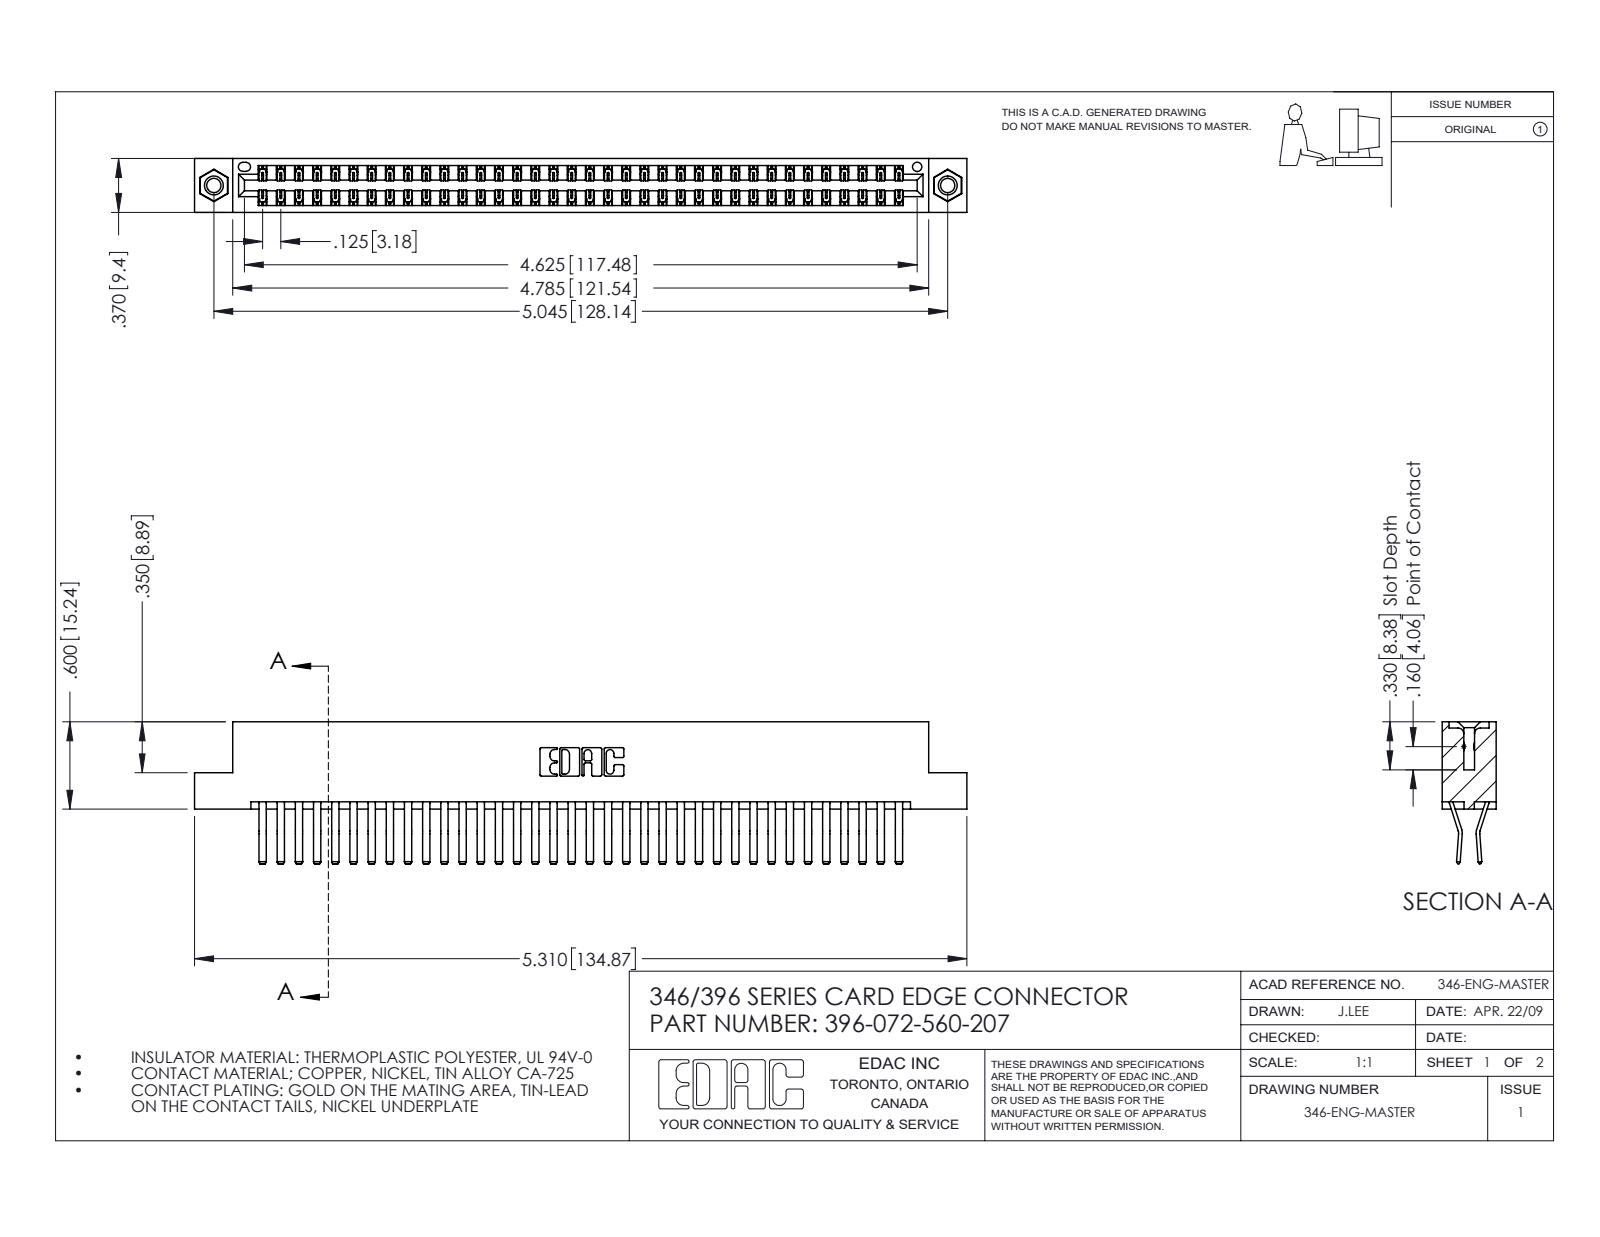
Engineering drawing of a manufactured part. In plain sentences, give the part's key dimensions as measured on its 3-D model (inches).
The part is named "396-072-560-207; 346 Part_Flush Mounting Lugs - 0.156 Dia-TI; 345-250-001_345-250-005-103; 345-292-001_560 Tail". Its 3-D file was written by "SolidWorks 2016 (CONFIG_CONTROL_DESIGN)". It is 75 solids with 4070 faces: 2628 planar, 1426 cylindrical and 16 other. Overall it measures 5.31 by 0.975 by 0.37 inches. Its volume is 0.828 cubic inches and its surface area 30.76 square inches. Round holes: 2 of diameter 0.098, 2 of diameter 0.125, 2 of diameter 0.156, 1 of diameter 0.064. Round bosses or shafts: 2 of diameter 0.155. Partial cylindrical surfaces (rounded edges, fillets, slot ends): 108 of radius 0.006, 22 of radius 0.01, 6 of radius 0.007, 6 of radius 0.031, 3 of radius 0.026, 2 of radius 0.01, 2 of radius 0.014, 2 of radius 0.022. The main face-to-face distances are 0.048, 0.322, 0.37, 0.025, 0.25, 0.072, 0.298, 0.275, 0.148, 0.222. The hole center spacings are 0.246, 4.836, 5.045.
